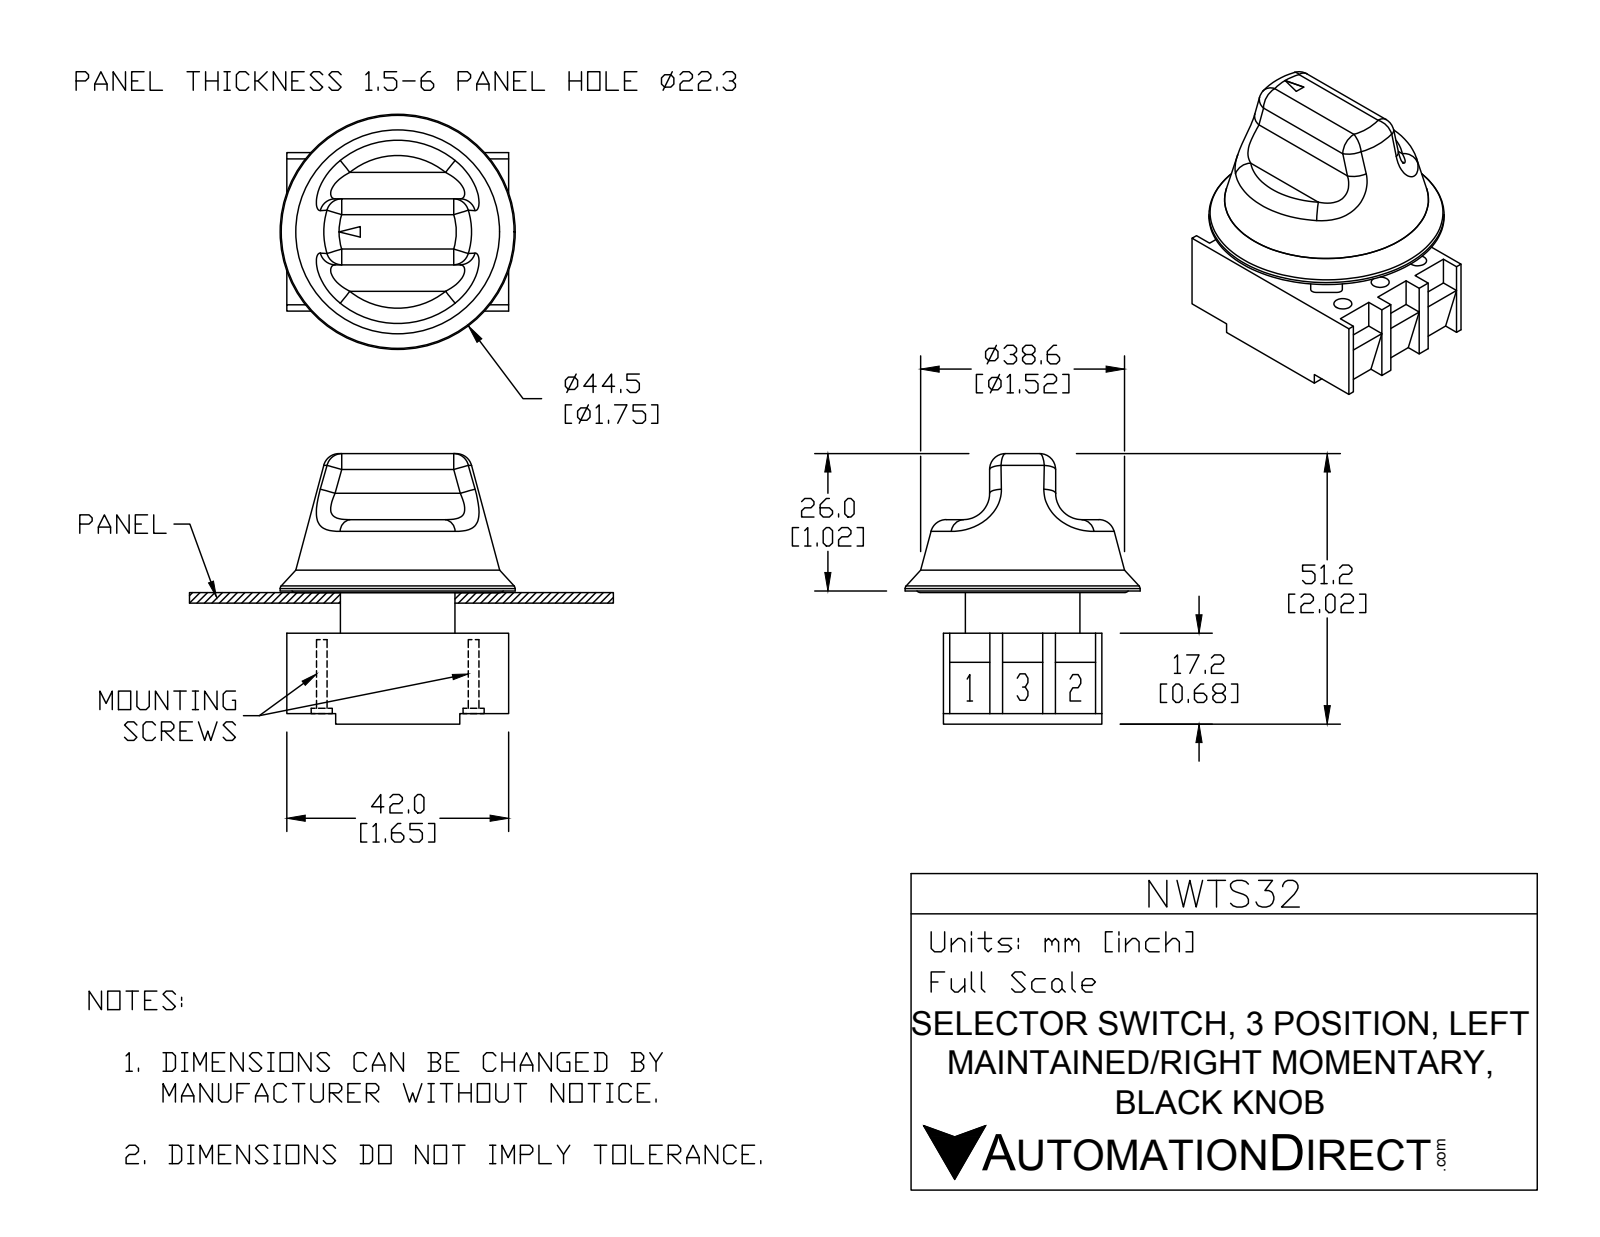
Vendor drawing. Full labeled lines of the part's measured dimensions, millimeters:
Part name (STEP PRODUCT): NWTS32
STEP written by: SolidWorks 2015 (AUTOMOTIVE_DESIGN)
Units: millimetres
Bodies: 7 solids, 236 faces (134 planar, 67 cylindrical, 35 other)
Overall size (bounding box): 51.2 × 44.5 × 44.5
Volume: 35 027 mm³ · Surface area: 19 099 mm²
Round holes (diameter × count): ⌀3.4 ×6, ⌀5 ×6, ⌀12.5 ×1
Round bosses / shafts (diameter × count): ⌀4.6 ×2, ⌀4 ×2, ⌀44.5 ×1, ⌀21.7 ×1
Partial cylindrical surfaces — rounded edges, fillets, slot ends (radius × count): R1 ×8, R8.7 ×5, R3 ×2, R5 ×2, R11 ×1
Main face-to-face distances: 3.95, 30, 8, 11.95, 7.7, 4.25, 10, 15.2, 22.9, 23.2
Hole centre spacings: 10, 17.52, 30.45, 28.76, 14.38, 20, 35.03
